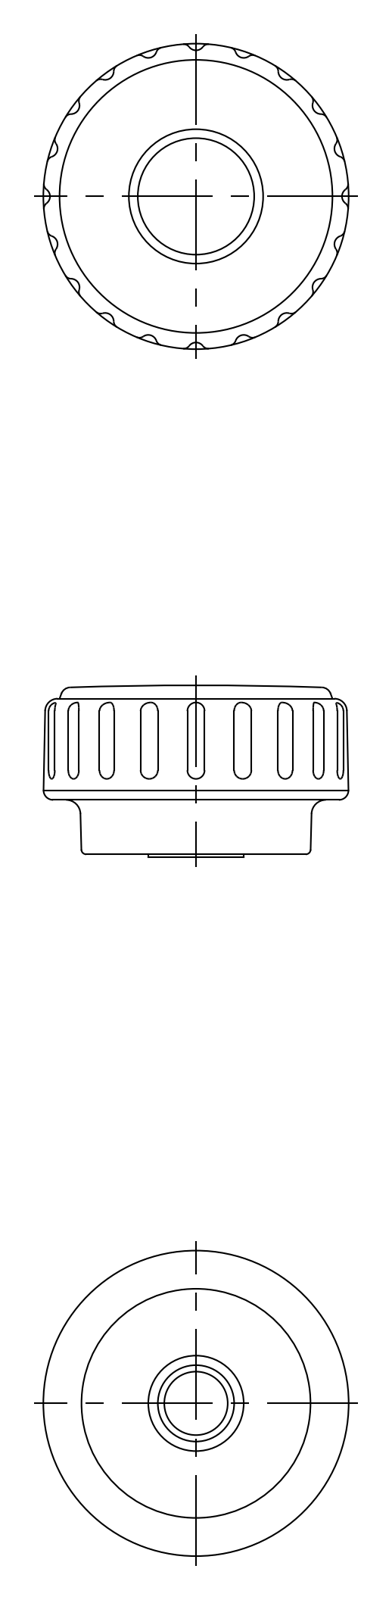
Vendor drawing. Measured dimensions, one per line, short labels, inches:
name: screw; knob; KDFS_32_M8_WH_2095_36
written by: CADfix (AUTOMOTIVE_DESIGN)
unit: in
bodies: 2 solids, 66 faces (0 planar, 0 cylindrical, 66 other)
size: 1.258 × 1.258 × 0.706
volume: 0.678 in³; area: 5.954 in²
